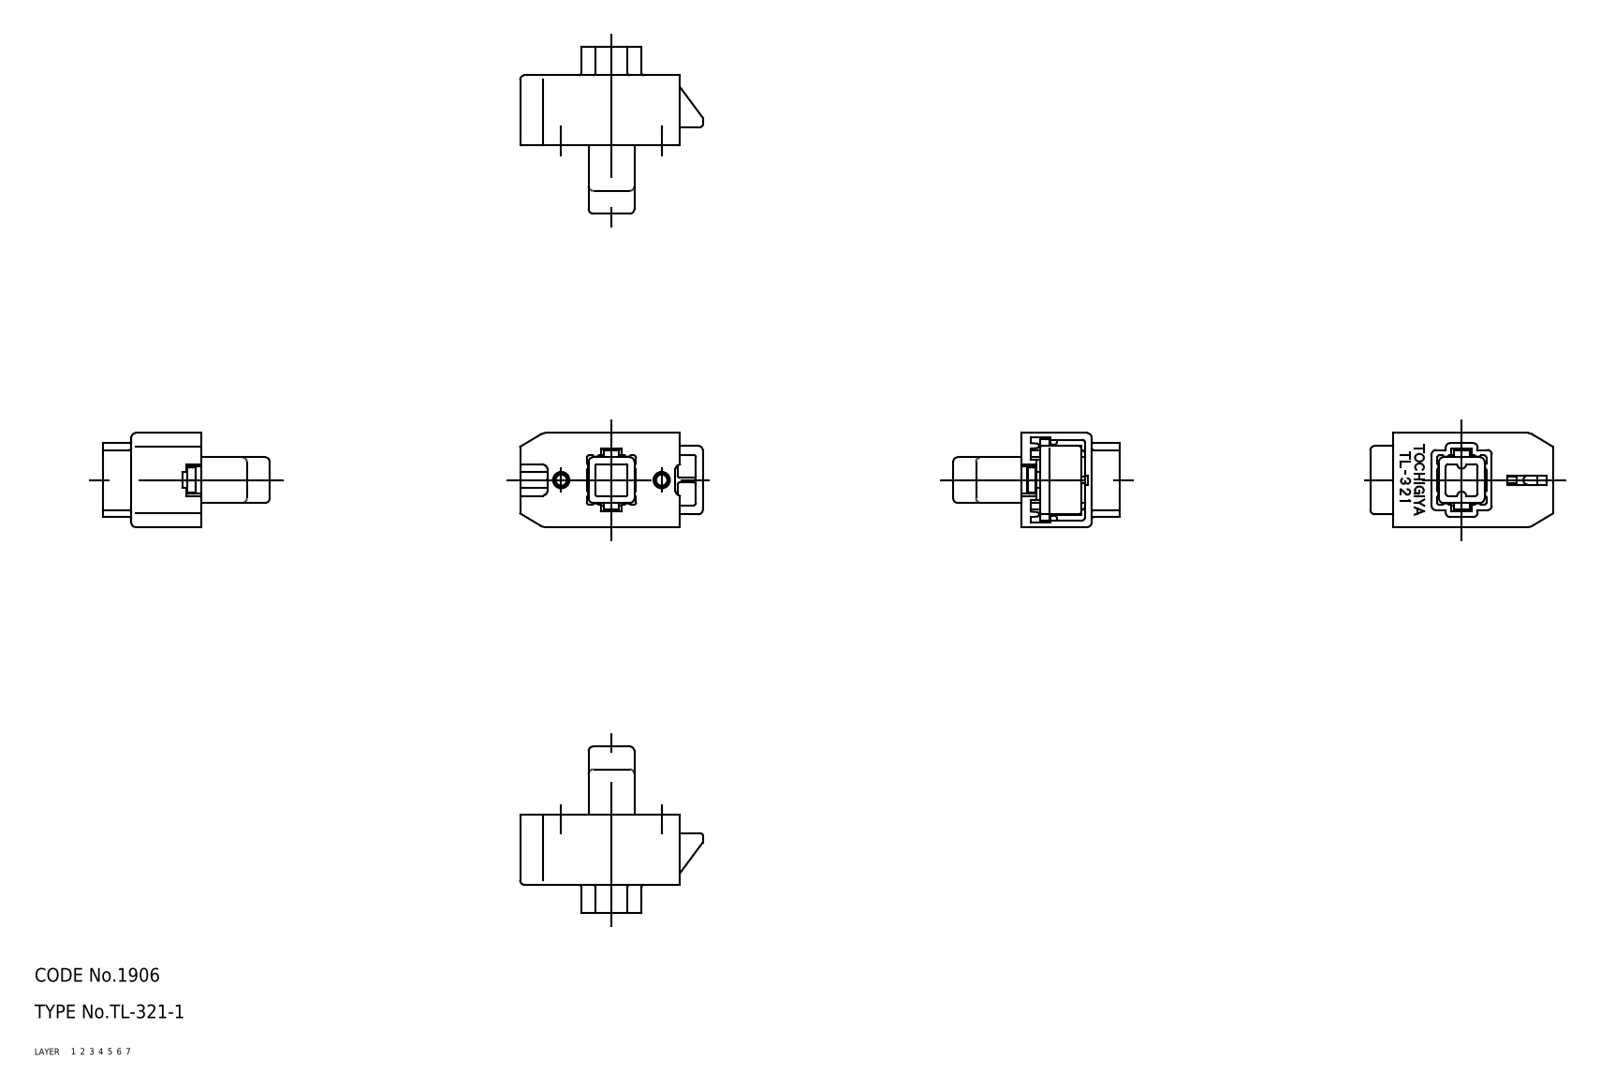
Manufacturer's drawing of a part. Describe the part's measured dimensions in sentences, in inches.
The part is named "nut; spring; latch; bouton (+2 more)". Its 3-D file was written by "CADfix (AUTOMOTIVE_DESIGN)". It is 6 solids with 396 faces: 0 planar, 0 cylindrical and 396 other. Overall it measures 1.575 by 1.437 by 0.811 inches. Its volume is 0.659 cubic inches and its surface area 15.31 square inches.
